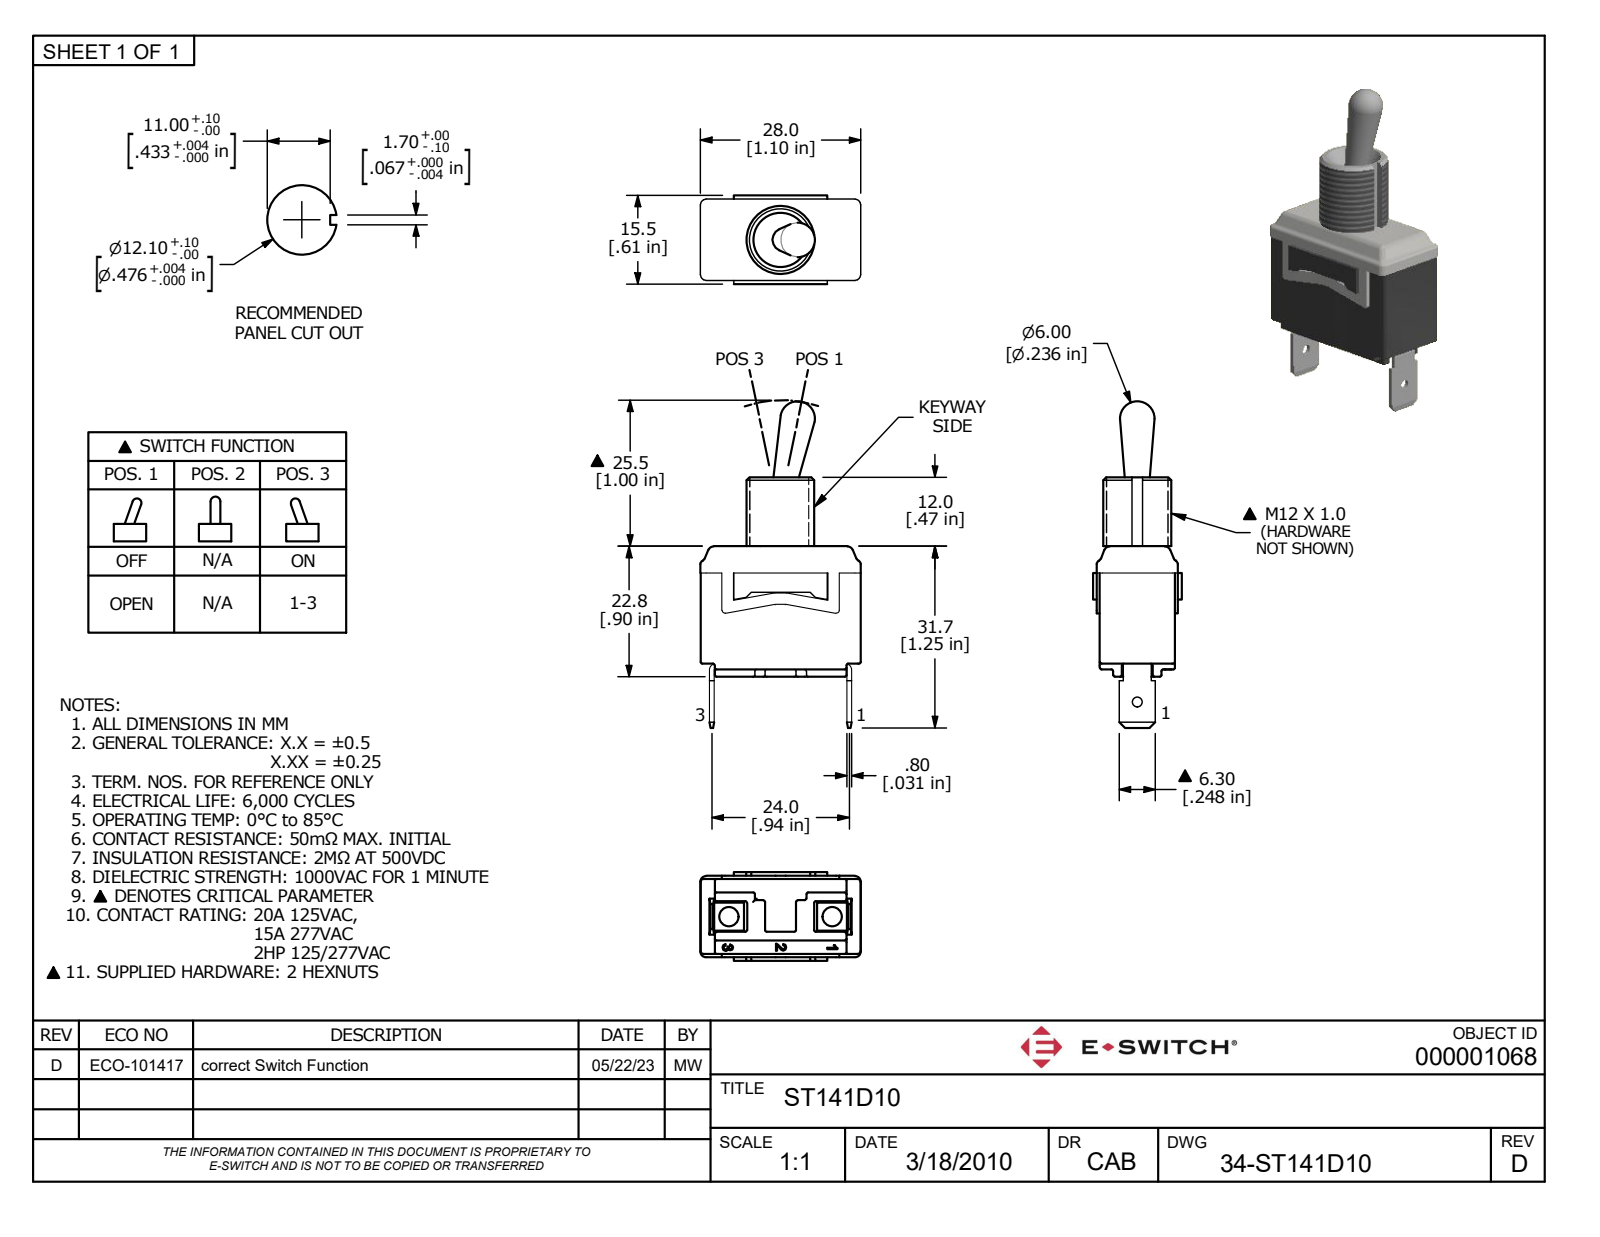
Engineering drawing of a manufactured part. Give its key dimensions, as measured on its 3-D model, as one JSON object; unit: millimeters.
{"part_name": "ST141D10", "step_written_by": "Autodesk Inventor 2022 (AUTOMOTIVE_DESIGN)", "units": "millimeters", "bodies": {"solids": 1, "faces": 383, "planar": 147, "cylindrical": 121, "other": 115}, "overall_size": [56.97, 28, 15.5], "volume_mm3": 9530, "surface_area_mm2": 3912, "round_holes": [[2, 2], [1.7, 1], [5.4, 1]], "round_bosses_or_shafts": [[11.91, 1]], "partial_cylinders_radius": [[0.3, 60], [1, 12], [0.5, 10], [0.6, 4], [0.8, 4], [1.1, 2]], "face_to_face_distances": [13.1, 0.55, 13.65, 27.94, 0.8, 1.2, 0.65, 14.3, 14.85, 21.5], "hole_center_spacings": [9, 18]}
